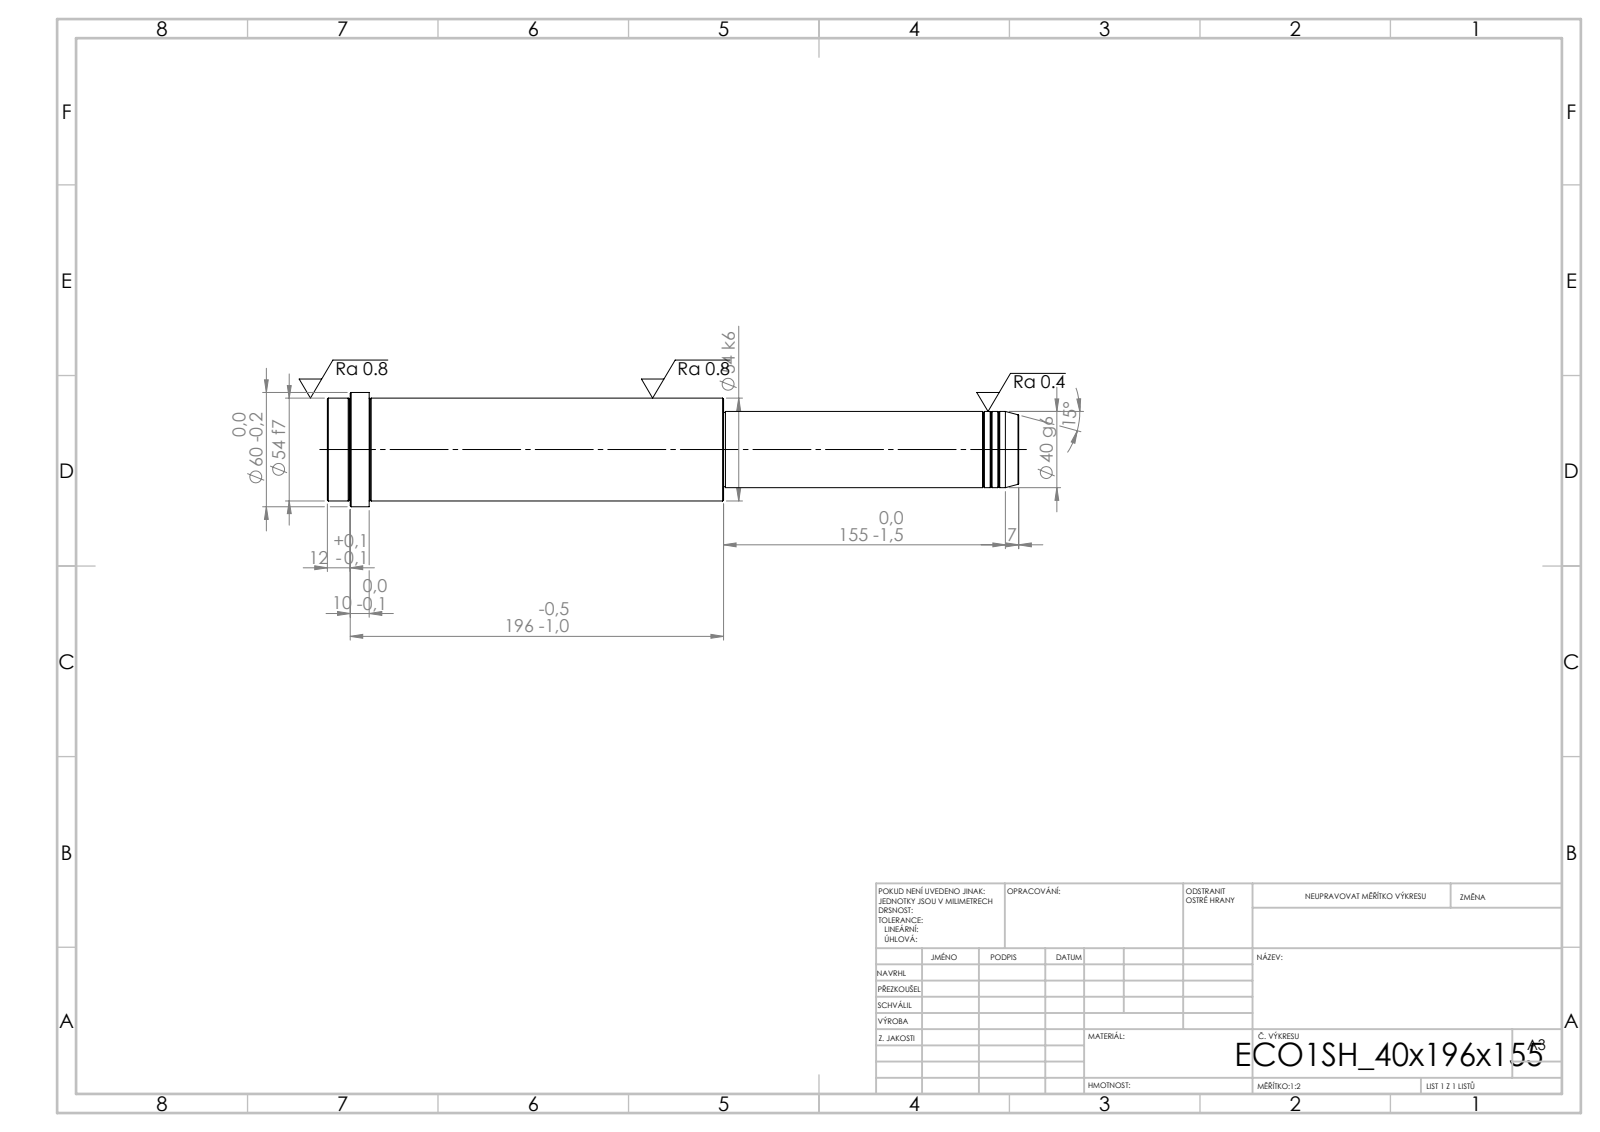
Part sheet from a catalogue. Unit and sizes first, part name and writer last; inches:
Units: inches
Overall size (bounding box): 14.291 × 2.362 × 2.362
Round bosses / shafts (diameter × count): ⌀2.362 ×1, ⌀2.126 ×1, ⌀1.575 ×1, ⌀1.535 ×1
Main face-to-face distances: 8.189, 6.102, 14.291, 13.425, 7.323, 0.866, 13.819, 7.717, 0.394, 0.472
Volume: 41.21 in³ · Surface area: 94.11 in²
Bodies: 1 solid, 52 faces (6 planar, 16 cylindrical, 30 other)
STEP written by: SolidWorks 2019 (CONFIG_CONTROL_DESIGN)
